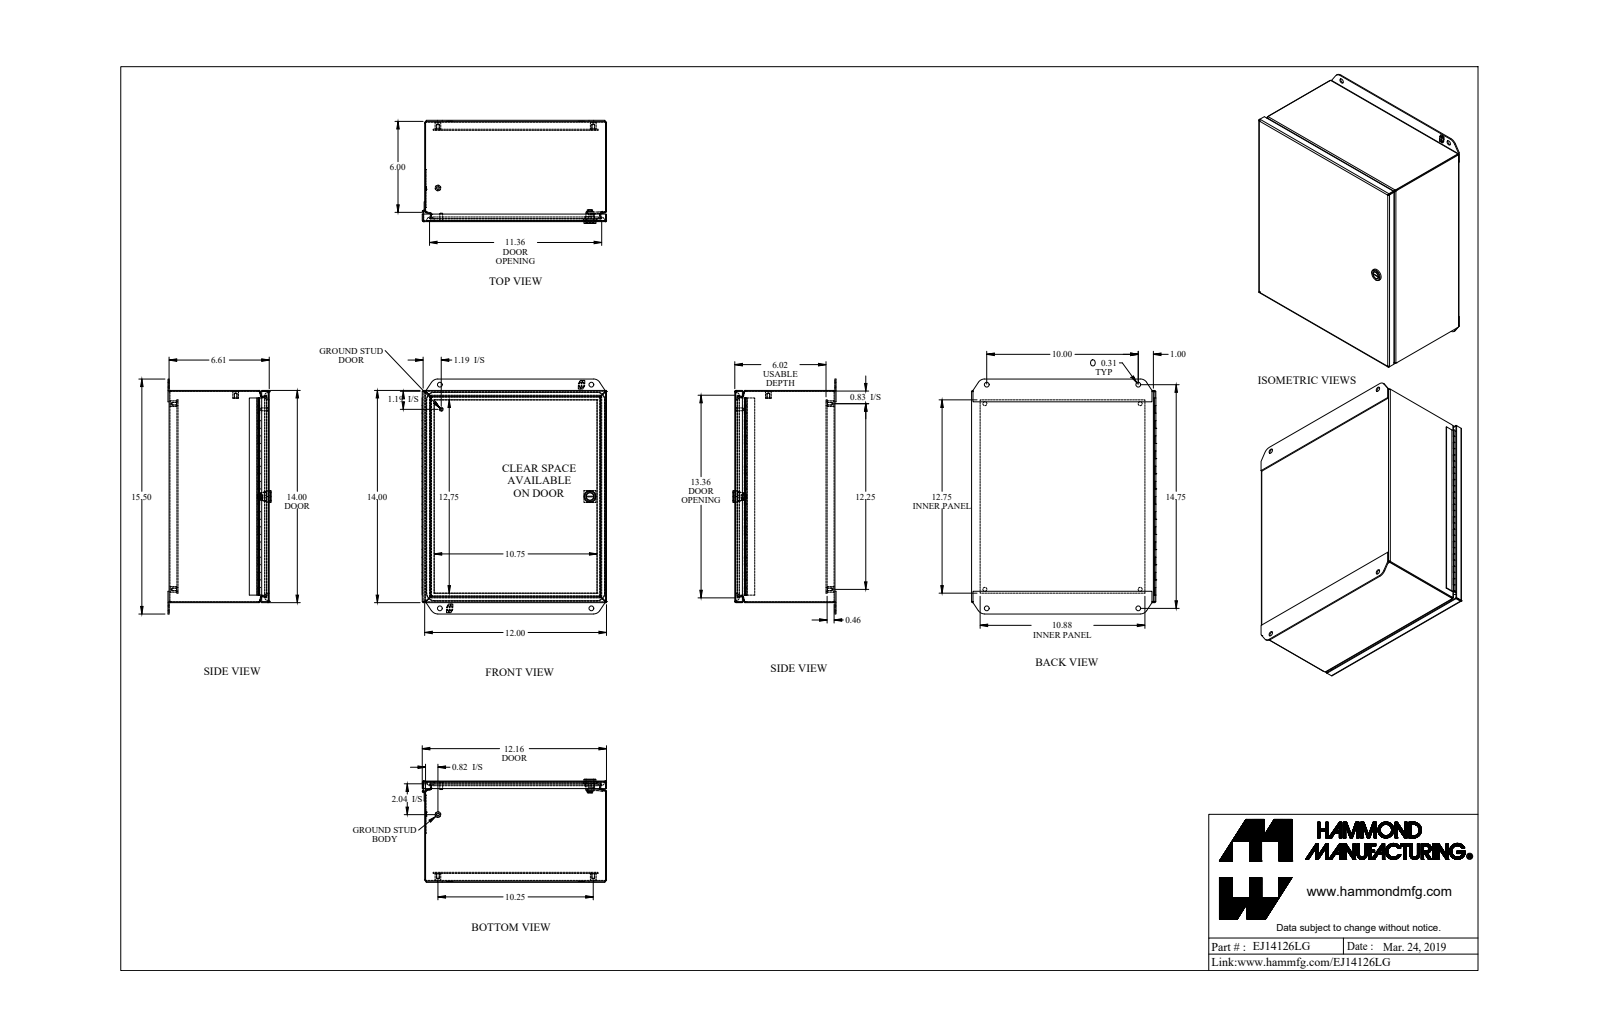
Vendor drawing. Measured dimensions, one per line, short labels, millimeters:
name: EJ14126LG_Default
written by: SolidWorks 2019 (CONFIG_CONTROL_DESIGN)
unit: mm
bodies: 16 solids, 739 faces (409 planar, 238 cylindrical, 92 other)
size: 393.7 × 309 × 172.8
volume: 954 200 mm³; area: 1 241 000 mm²
holes: 5× ⌀4, 4× ⌀6.7, 4× ⌀8, 1× ⌀1.3, 1× ⌀13.1
bosses: 5× ⌀9.5, 1× ⌀20, 1× ⌀13.6, 1× ⌀12.6, 1× ⌀11, 1× ⌀6.4, 1× ⌀4.8, 1× ⌀2.5
rounds: 16× R0.7, 16× R2.2, 10× R7.1, 4× R6.4, 4× R12.7, 4× R12.7, 2× R1.5, 2× R13.7
face distances: 1.4, 166.5, 1.8, 15, 167.9, 165, 303.4, 354.2, 11.7, 13.1
hole spacings: 311.2, 155.7, 259.1, 405.7, 31.9, 31.9, 342.9, 342.9
